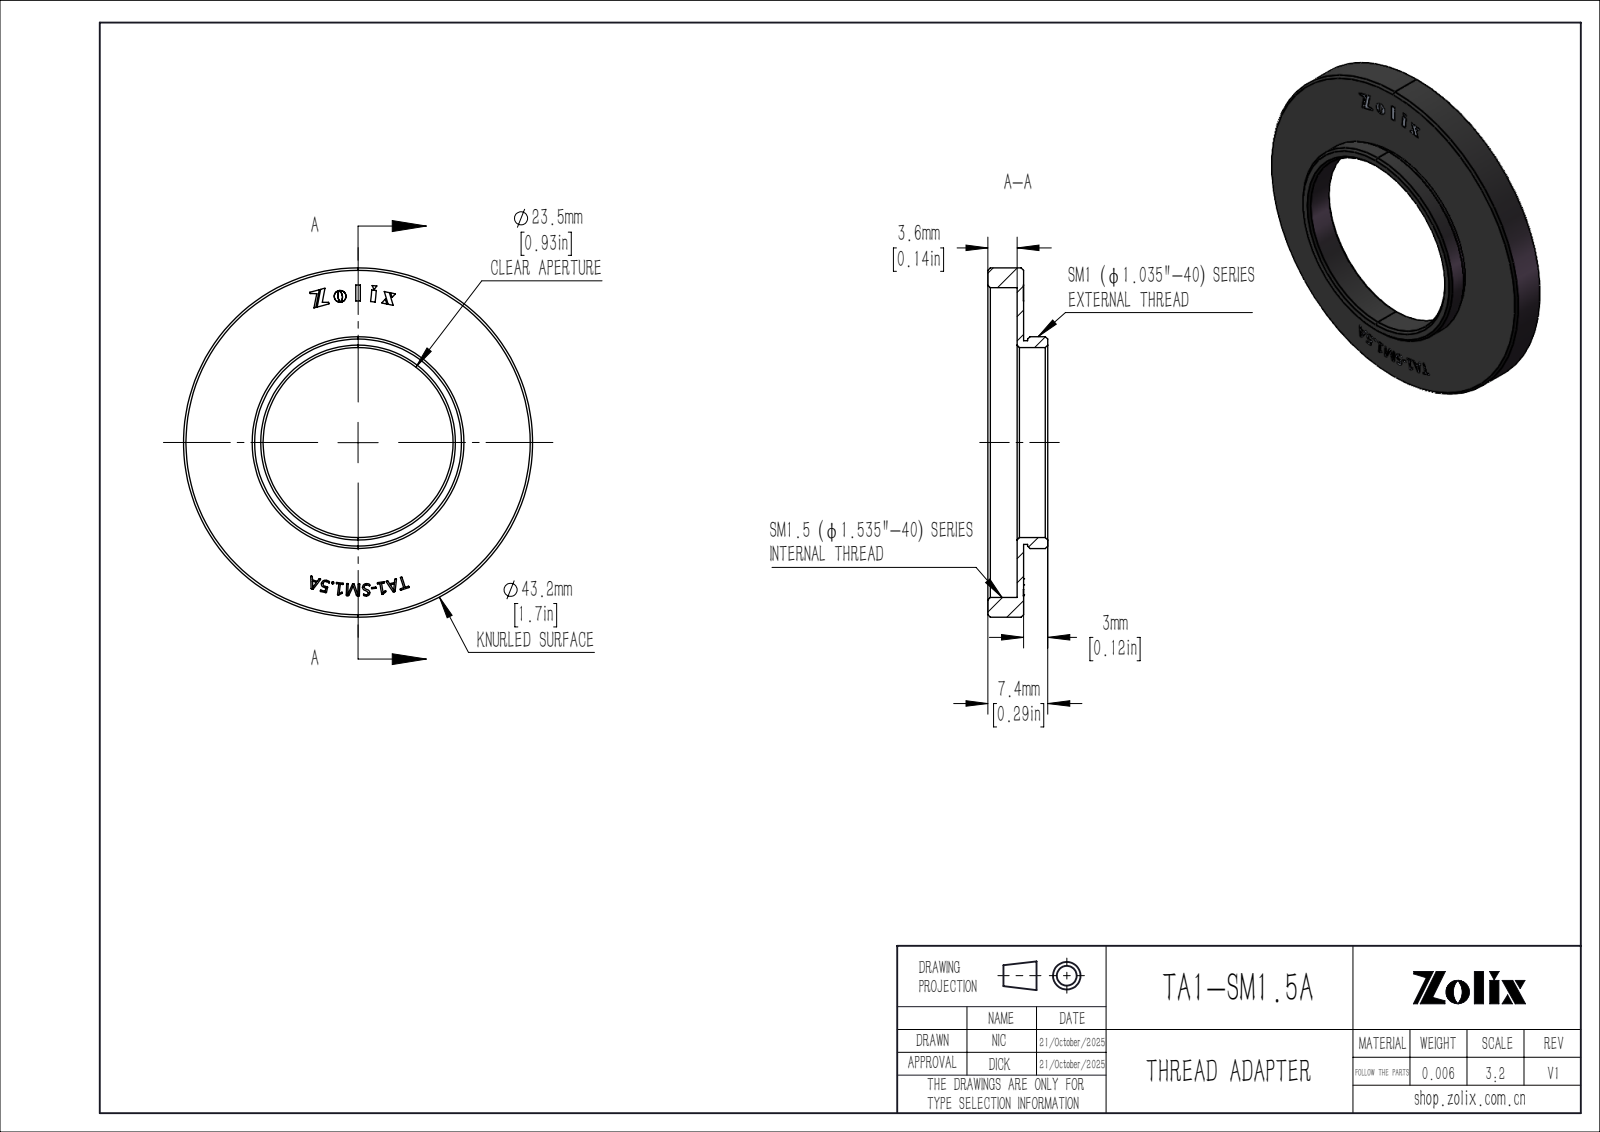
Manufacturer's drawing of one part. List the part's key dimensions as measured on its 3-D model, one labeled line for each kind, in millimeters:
Part name (STEP PRODUCT): TA1-SM1.5A
STEP written by: SolidWorks 2020 (CONFIG_CONTROL_DESIGN)
Units: millimetres
Bodies: 1 solid, 336 faces (226 planar, 10 cylindrical, 100 other)
Overall size (bounding box): 43.2 × 43.2 × 7.4
Volume: 2 219 mm³ · Surface area: 3 579 mm²
Round holes (diameter × count): ⌀23.5 ×1, ⌀38.3 ×1
Round bosses / shafts (diameter × count): ⌀43.2 ×1, ⌀26.2 ×1, ⌀25.2 ×1
Main face-to-face distances: 0.8, 3.6, 4.4, 7.4, 3.8, 3, 4.9, 1.3, 0.5, 2.5
